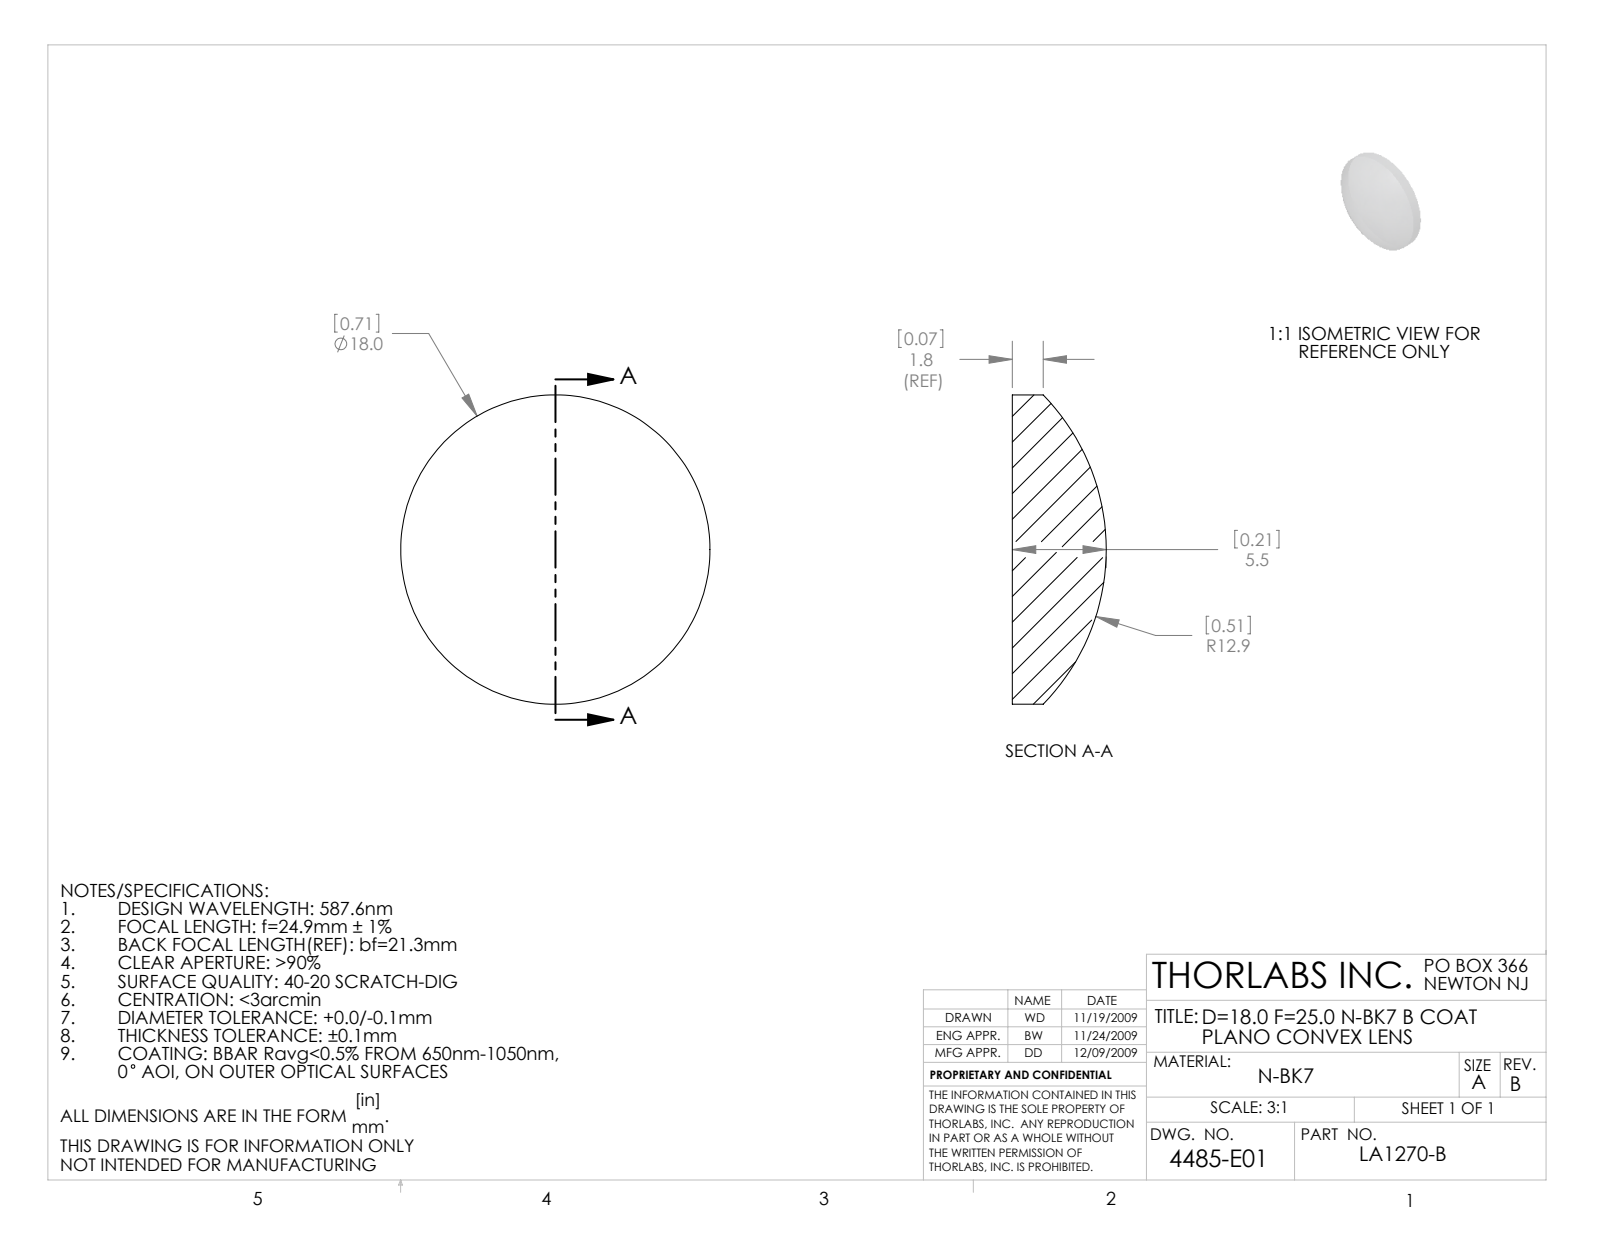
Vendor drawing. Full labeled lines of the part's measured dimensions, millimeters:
Part name (STEP PRODUCT): 4485-E0W
STEP written by: SolidWorks 2009 (AUTOMOTIVE_DESIGN)
Units: millimetres
Bodies: 1 solid, 5 faces (1 planar, 2 cylindrical, 2 other)
Overall size (bounding box): 18 × 18 × 5.46
Volume: 948 mm³ · Surface area: 652 mm²
Round bosses / shafts (diameter × count): ⌀18 ×1
